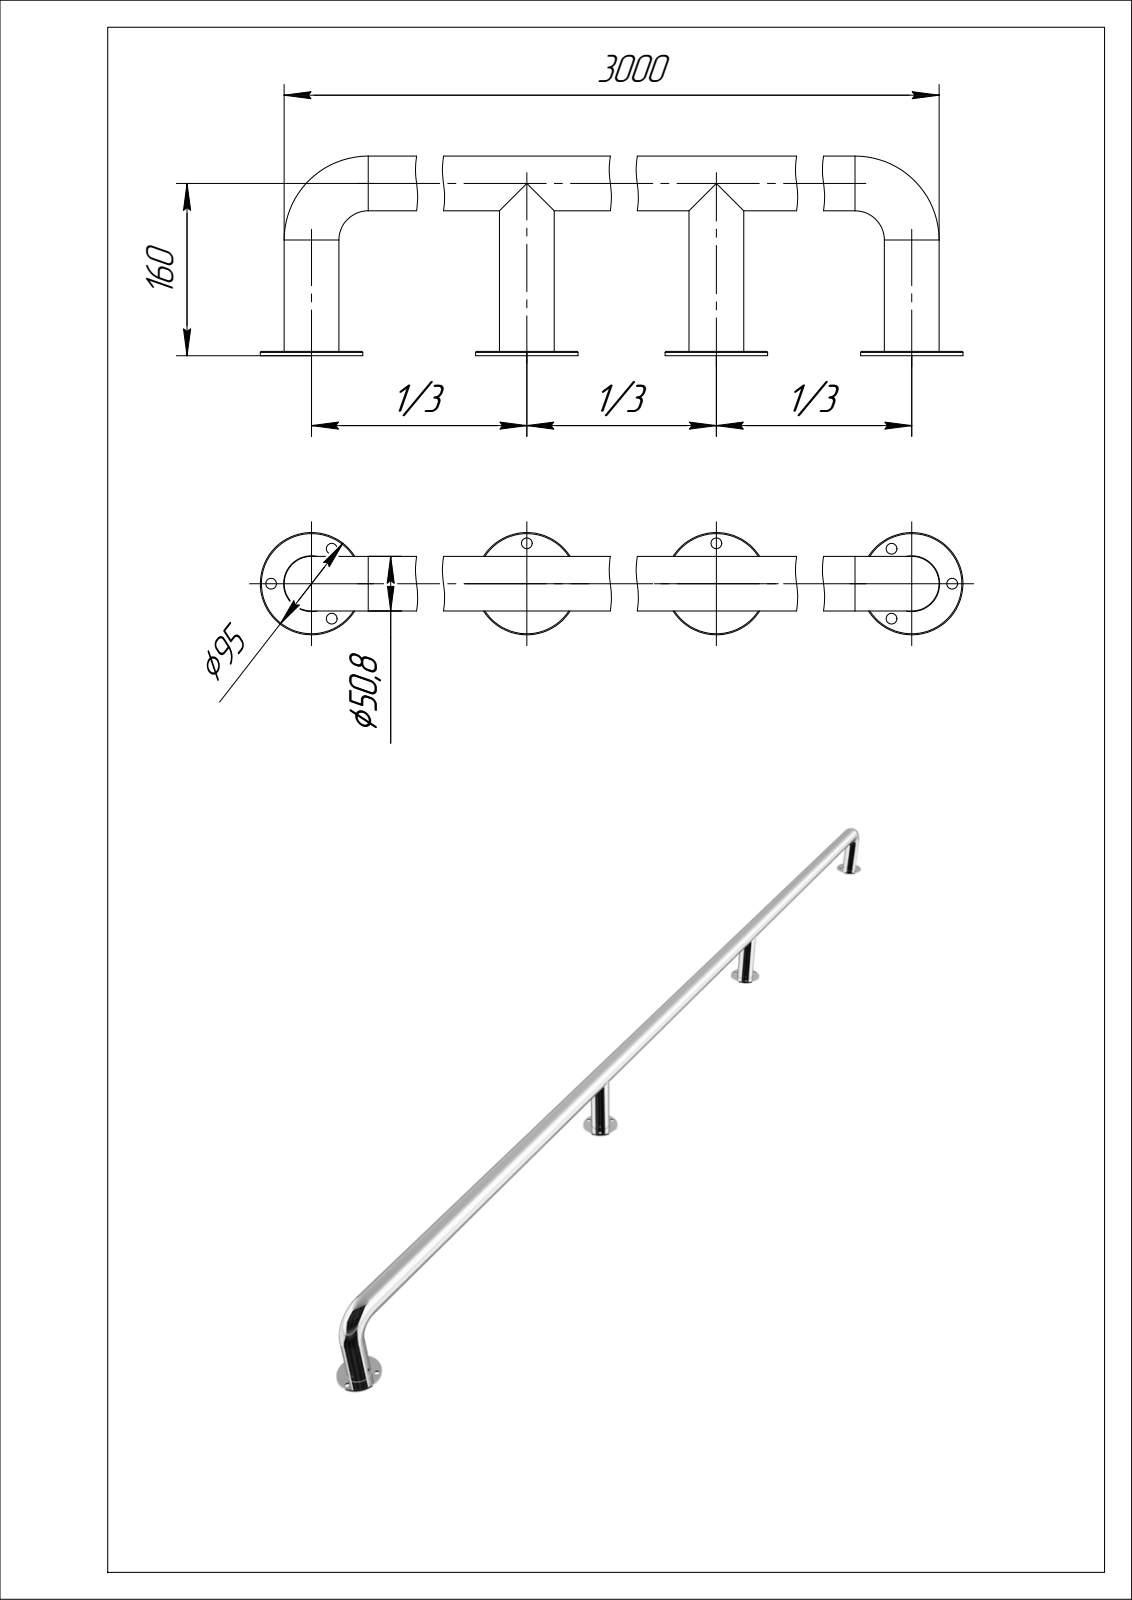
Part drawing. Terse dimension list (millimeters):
name: Сборка; Деталь; Фланец; Тр 2-42.5
written by: ASCON Math Kernel (AUTOMOTIVE_DESIGN)
unit: mm
bodies: 11 solids, 72 faces (20 planar, 38 cylindrical, 14 other)
size: 3044.2 × 185.4 × 95
volume: 689 386 mm³; area: 1 163 000 mm²
holes: 12× ⌀10, 3× ⌀48.8, 2× ⌀6, 2× ⌀47.8, 2× ⌀51.8, 1× ⌀50.8
bosses: 4× ⌀95, 4× ⌀50.8, 2× ⌀39
face distances: 4, 12, 8, 170, 166, 158
hole spacings: 37.5, 64.95, 64.96, 965.13, 982.54, 1947.39, 2930.63, 2968.13
